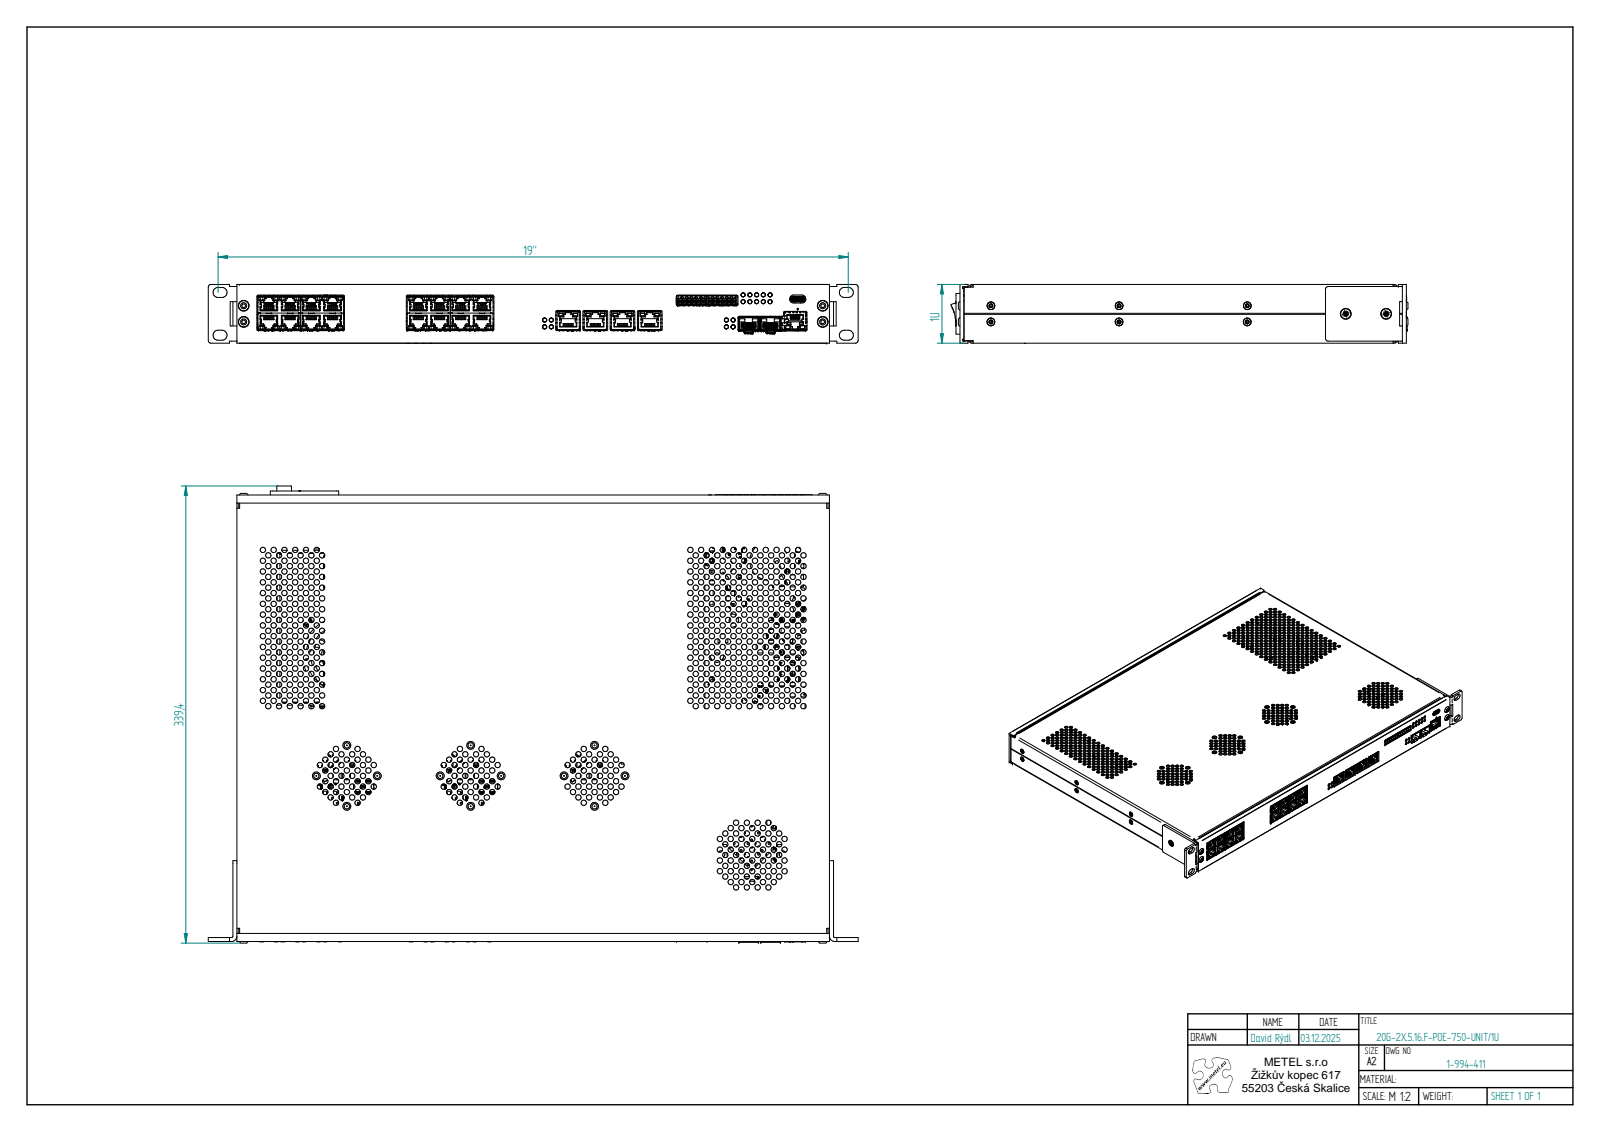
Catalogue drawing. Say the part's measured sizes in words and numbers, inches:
The part is named "20G-2X.5.16; M3x6 zap; PWR; X2_0 (+8 more)". Its 3-D file was written by "Solid Edge (AUTOMOTIVE_DESIGN)". It is 96 solids with 20467 faces: 14477 planar, 4746 cylindrical and 1244 other. Overall it measures 19 by 13.361 by 1.717 inches. Its volume is 36 cubic inches and its surface area 1 381 square inches. Round holes: 742 of diameter 0.157, 21 of diameter 0.122, 16 of diameter 0.118, 8 of diameter 0.097, 7 of diameter 0.128, 6 of diameter 0.315, 4 of diameter 0.018, 4 of diameter 0.102, 4 of diameter 0.165, 2 of diameter 0.016, 2 of diameter 0.02, 2 of diameter 0.177. Round bosses or shafts: 24 of diameter 0.118, 24 of diameter 0.059, 12 of diameter 0.071, 10 of diameter 0.108, 6 of diameter 0.157, 2 of diameter 0.295, 2 of diameter 0.139, 2 of diameter 0.018. Partial cylindrical surfaces (rounded edges, fillets, slot ends): 299 of radius 0.004, 287 of radius 0.008, 166 of radius 0.01, 98 of radius 0.012, 94 of radius 0.039, 81 of radius 0.006, 79 of radius 0.016, 68 of radius 0.01. The main face-to-face distances are 0.039, 1.678, 1.639, 1.717, 0.118, 17.283, 12.933, 17.244, 17.323, 0.315. The hole center spacings are 0.223, 0.315, 0.498, 0.63, 0.803, 0.945, 1.113, 1.26.
